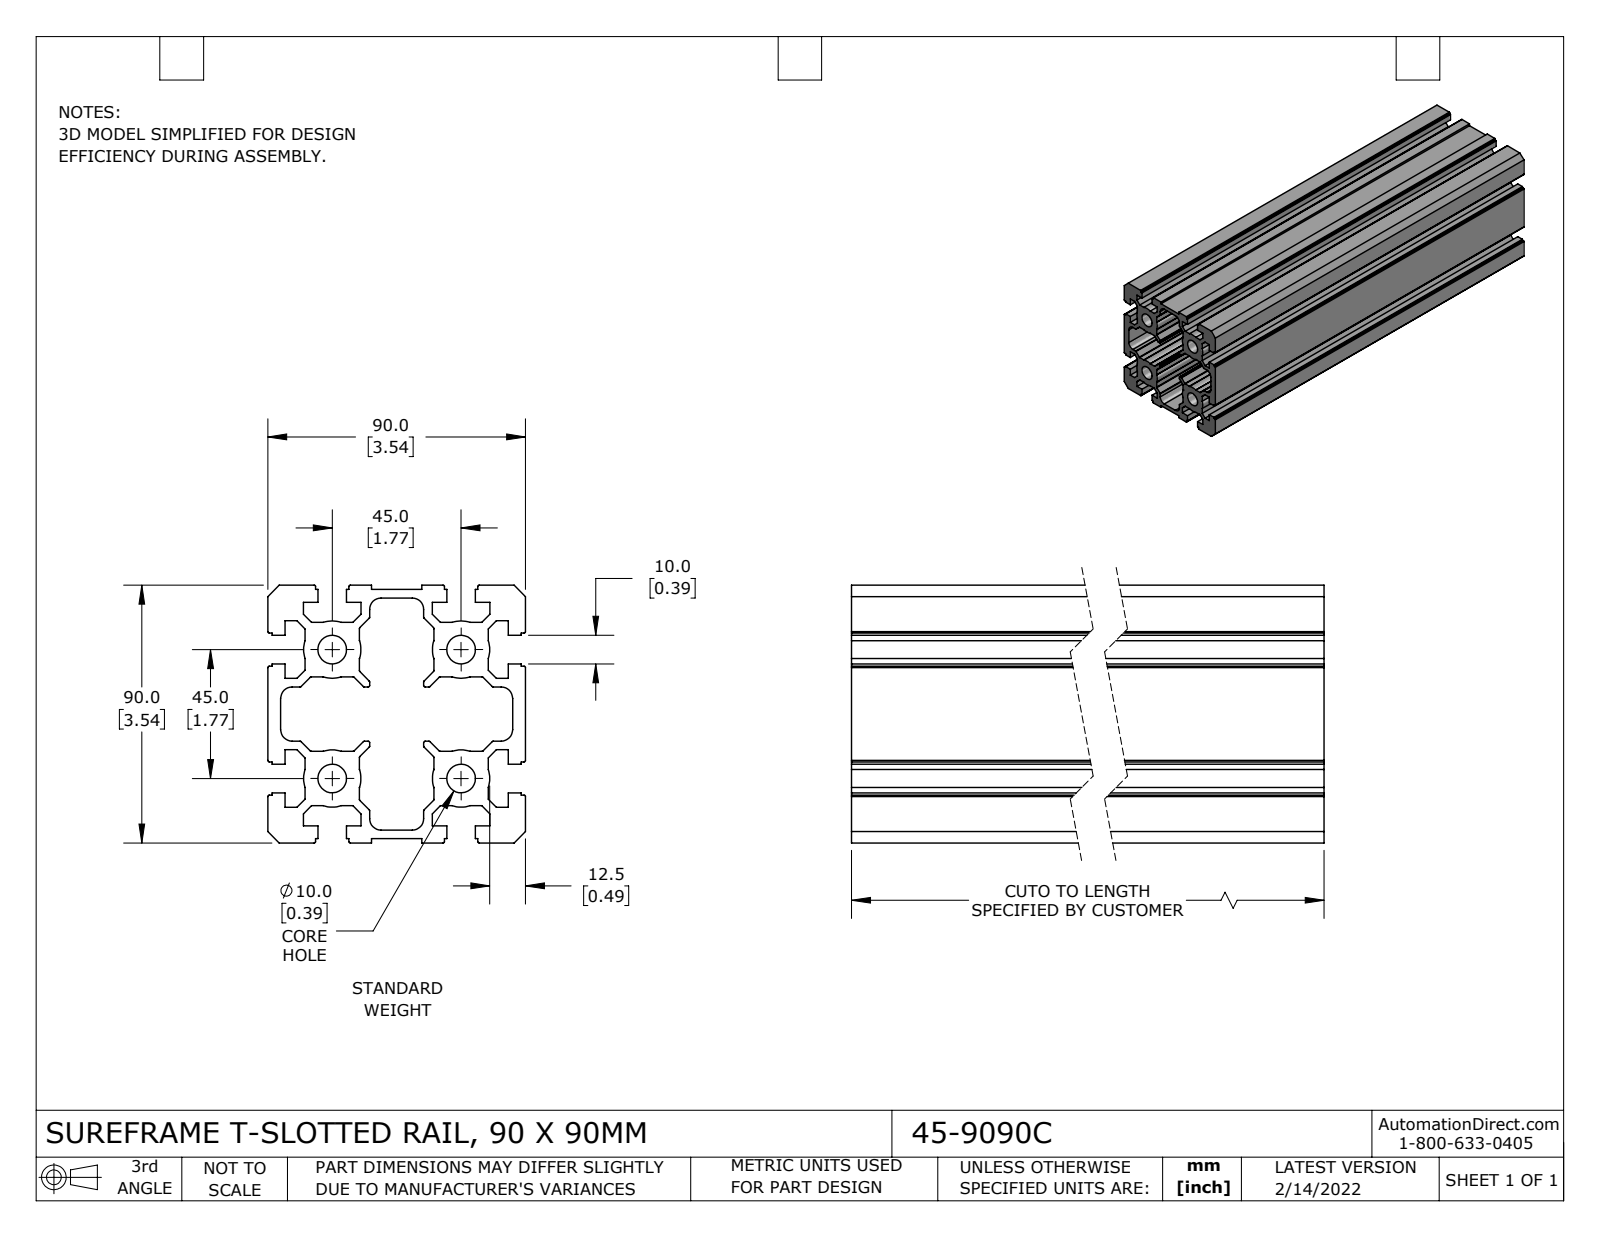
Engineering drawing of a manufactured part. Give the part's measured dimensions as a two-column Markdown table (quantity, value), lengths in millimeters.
| quantity | value |
| --- | --- |
| part name | 45-9090C |
| STEP written by | SolidWorks 2021 (CONFIG_CONTROL_DESIGN) |
| units | millimeters |
| bodies | 1 solid, 292 faces (190 planar, 102 cylindrical, 0 other) |
| overall size | 304.8 × 90 × 90 |
| volume | 905 018 mm³ |
| surface area | 358 201 mm² |
| round holes (diameter × count) | 10 × 4 |
| partial cylindrical surfaces (radius × count) | 0.51 × 52, 0.5 × 16, 4 × 8, 10 × 4 |
| main face-to-face distances | 4.5, 45, 26, 84, 58, 13, 90, 1.5, 71, 6 |
| hole center spacings | 45, 63.64 |
